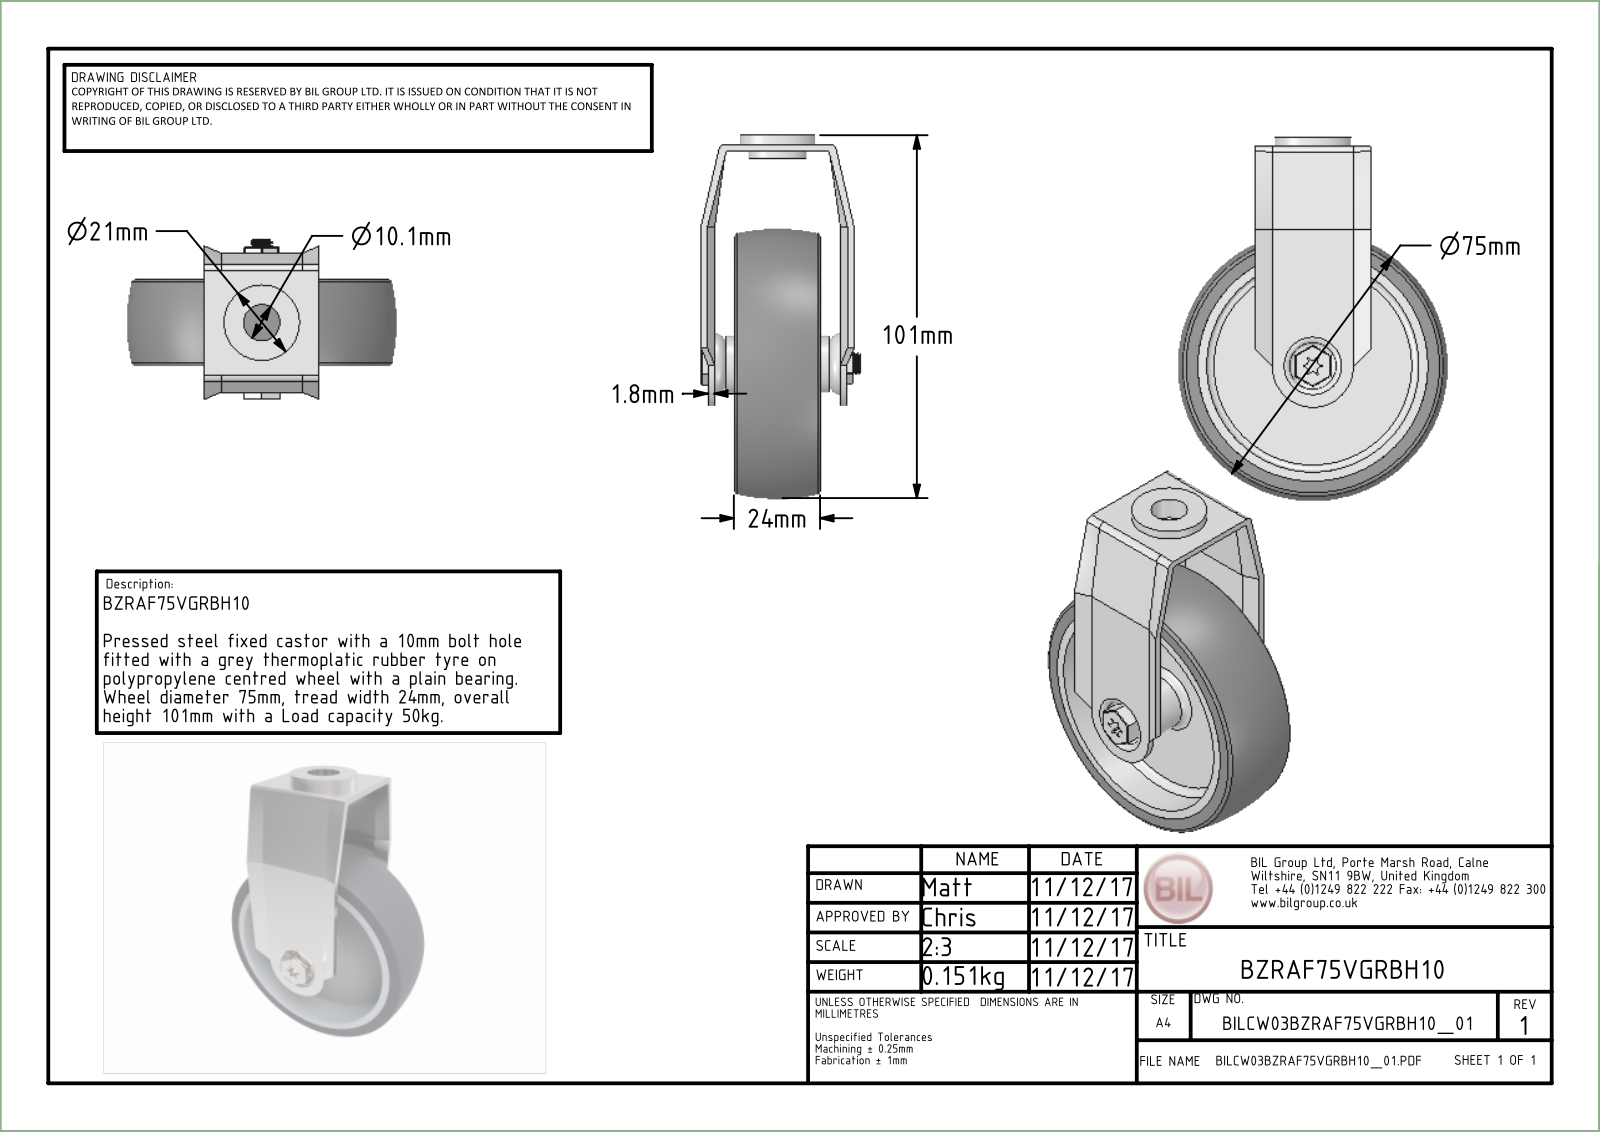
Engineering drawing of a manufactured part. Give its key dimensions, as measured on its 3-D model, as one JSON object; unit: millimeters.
{"part_name": "BZRAF75VGRBH10 v3; BZRAF75ASBH10 v1; ZINC PLATED PRESSED STEEL FORKS; BZL75WVGR8 v1 (+8 more)", "step_written_by": "Autodesk Translation Framework v13.20.0.188 (AP242_MANAGED_MODEL_BASED_3D_ENGINEERING_MIM_LF)", "units": "millimeters", "bodies": {"solids": 6, "faces": 285, "planar": 76, "cylindrical": 99, "other": 110}, "overall_size": [101, 75, 44.75], "volume_mm3": 75585, "surface_area_mm2": 42536, "round_holes": [[6, 1], [6.2, 1], [6.4, 1], [8.2, 1], [8.4, 1], [10.2, 1], [54, 1], [60, 1]], "round_bosses_or_shafts": [[21, 1], [16, 1], [8, 1], [5.88, 1], [4.74, 1]], "partial_cylinders_radius": [[1, 26], [0.5, 12], [1.5, 8], [0.4, 6], [0.99, 4], [1.8, 2], [2.12, 1], [11.91, 1]], "face_to_face_distances": [1.8, 10, 14, 35.8, 1, 5.5, 15.5, 19.5, 29.5, 24]}
